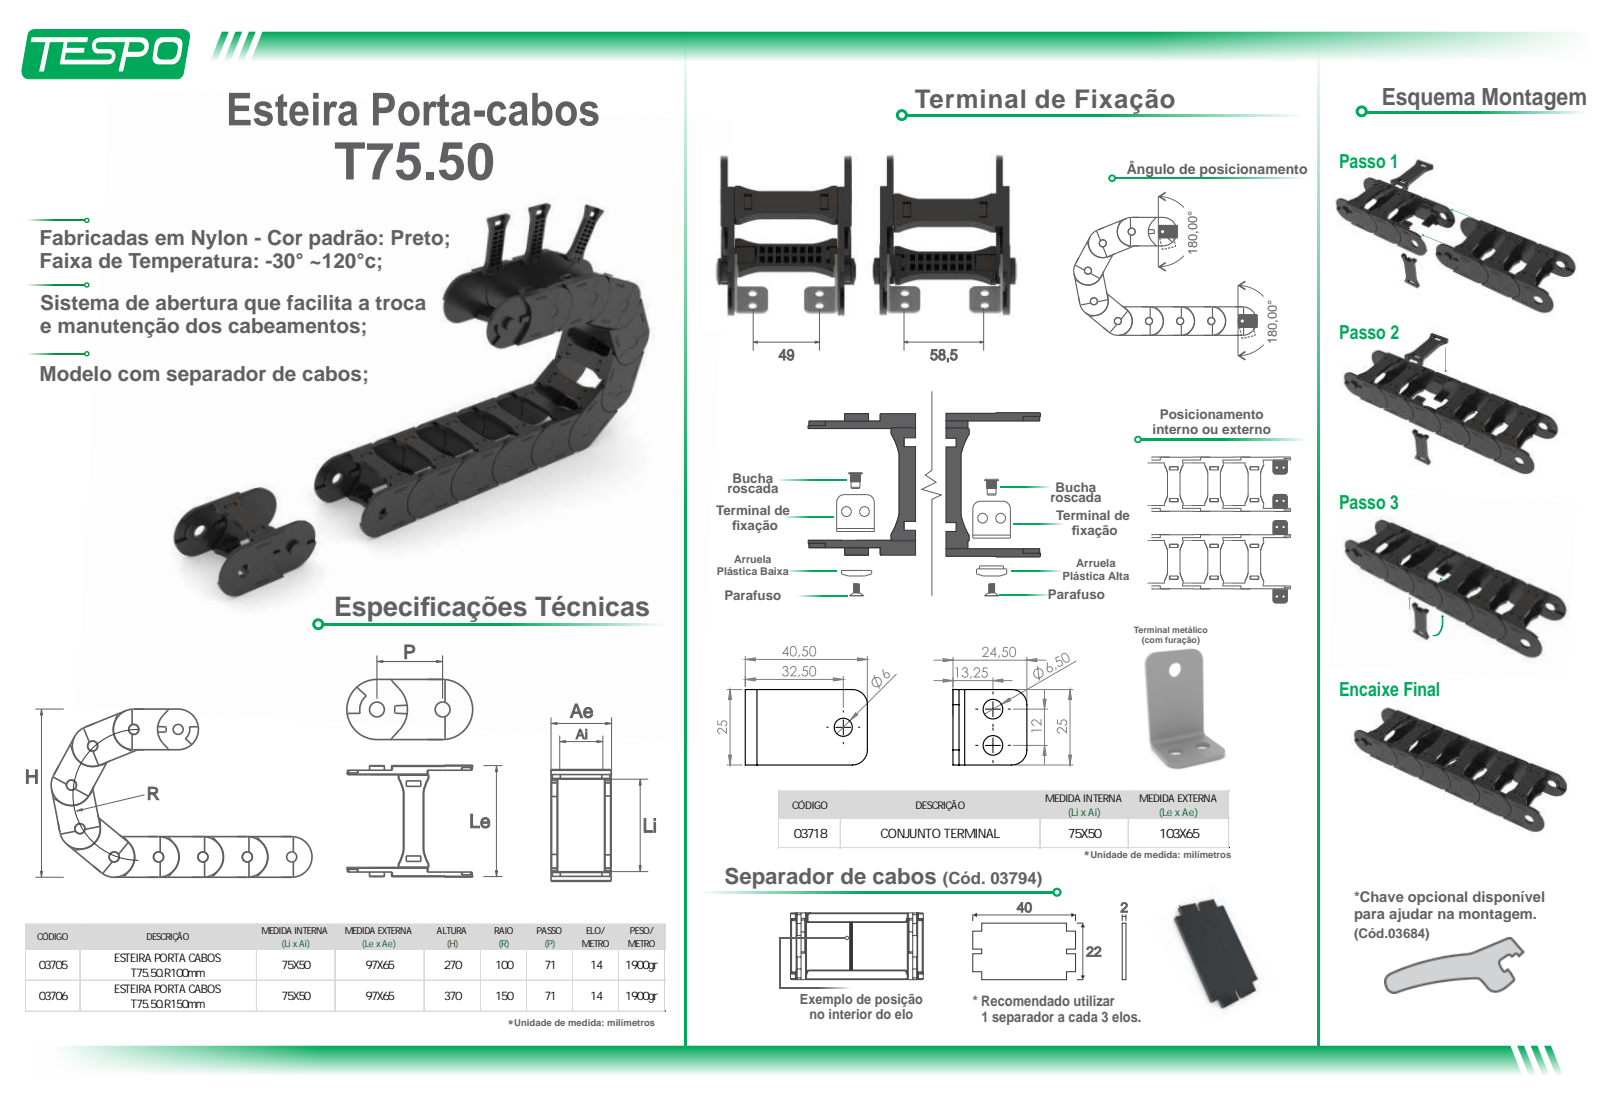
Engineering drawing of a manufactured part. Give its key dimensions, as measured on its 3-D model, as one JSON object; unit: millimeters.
{"step_written_by": "ST-DEVELOPER v15 (AUTOMOTIVE_DESIGN)", "units": "millimeters", "bodies": {"solids": 4, "faces": 150, "planar": 0, "cylindrical": 0, "other": 150}, "overall_size": [136, 95, 65], "volume_mm3": 116576, "surface_area_mm2": 51040}
